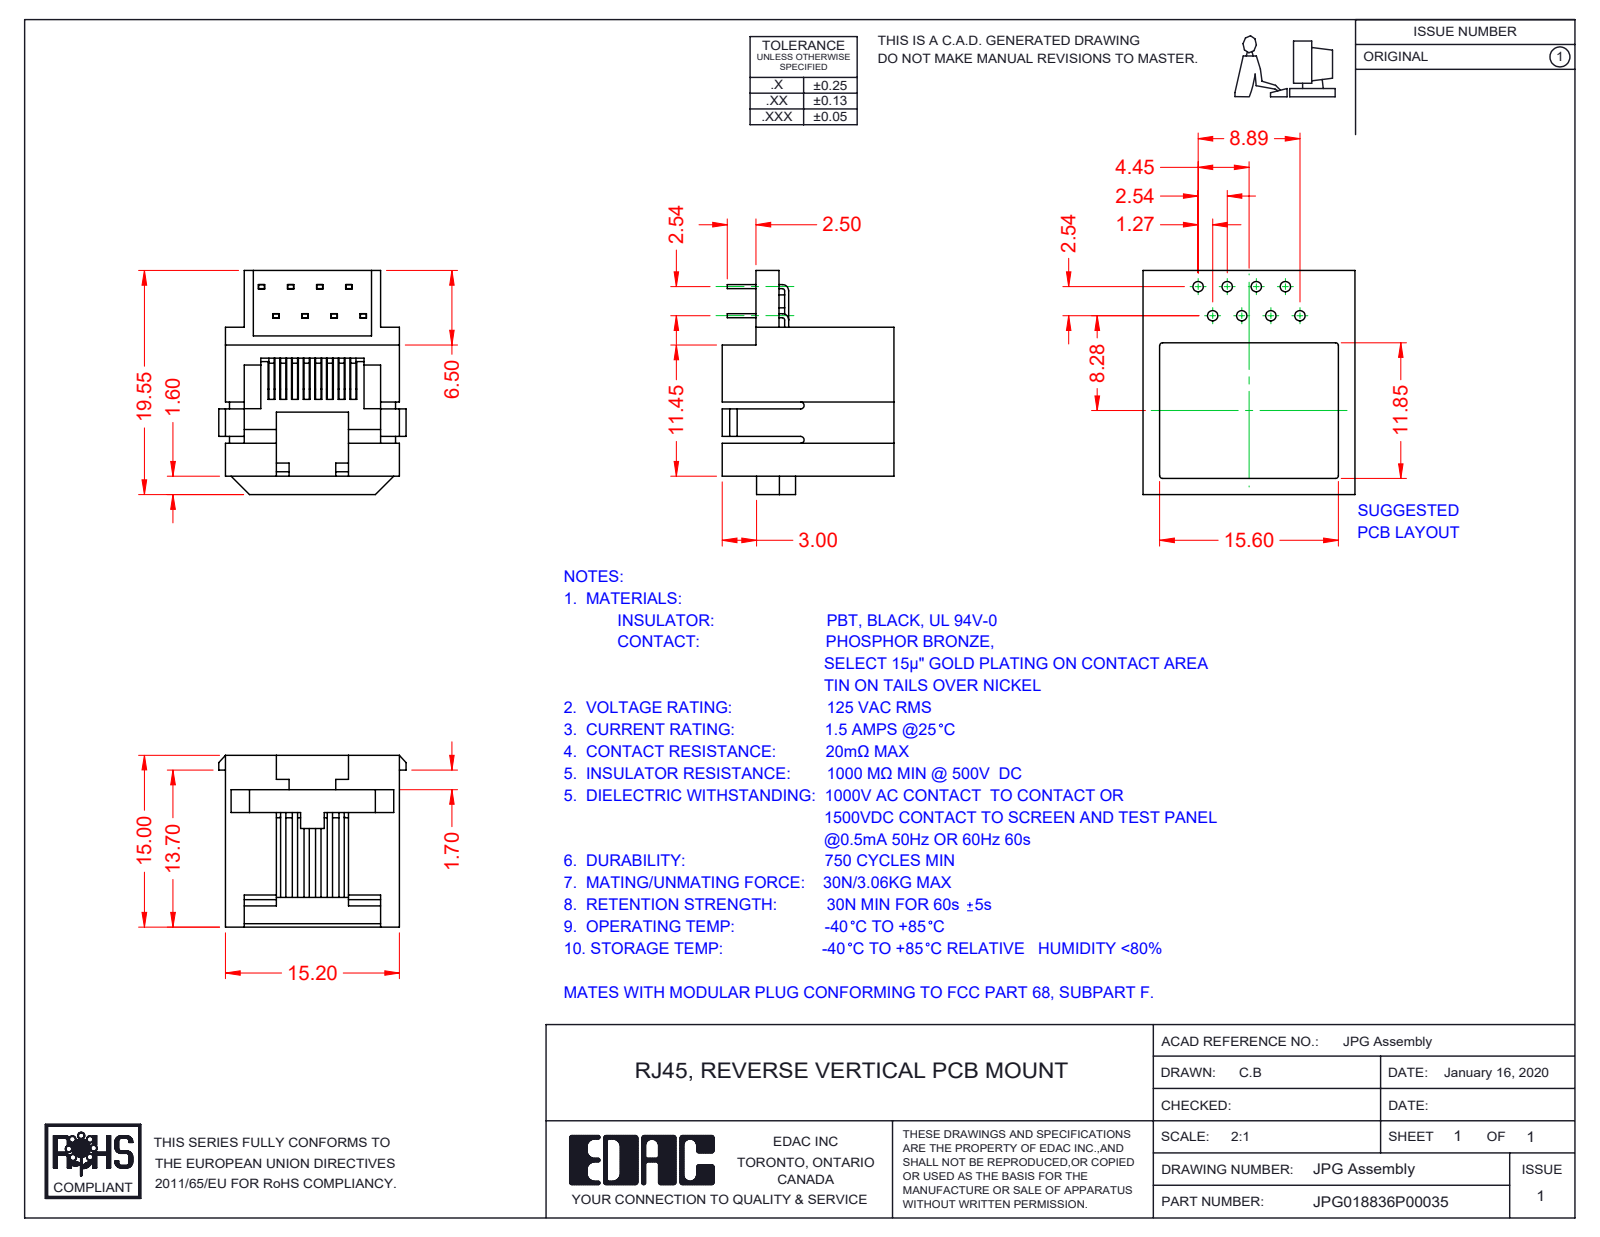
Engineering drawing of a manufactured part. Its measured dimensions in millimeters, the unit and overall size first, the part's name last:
Units: millimetres
Overall size (bounding box): 19.55 × 16.35 × 15
Partial cylindrical surfaces — rounded edges, fillets, slot ends (radius × count): R0.3 ×3, R0.2 ×2, R0.35 ×2, R0.55 ×2, R0.7 ×2
Main face-to-face distances: 0.35, 1.64, 13.56, 10.3, 15.2, 2.6, 1.8, 0.6, 1.35, 12.9
Volume: 1 392 mm³ · Surface area: 2 707 mm²
Bodies: 10 solids, 542 faces (461 planar, 69 cylindrical, 12 other)
Part name (STEP PRODUCT): PG Contacts; PG Contact Lock; JPG018836P00035; PG Insulator
STEP written by: SolidWorks 2016 (CONFIG_CONTROL_DESIGN)
